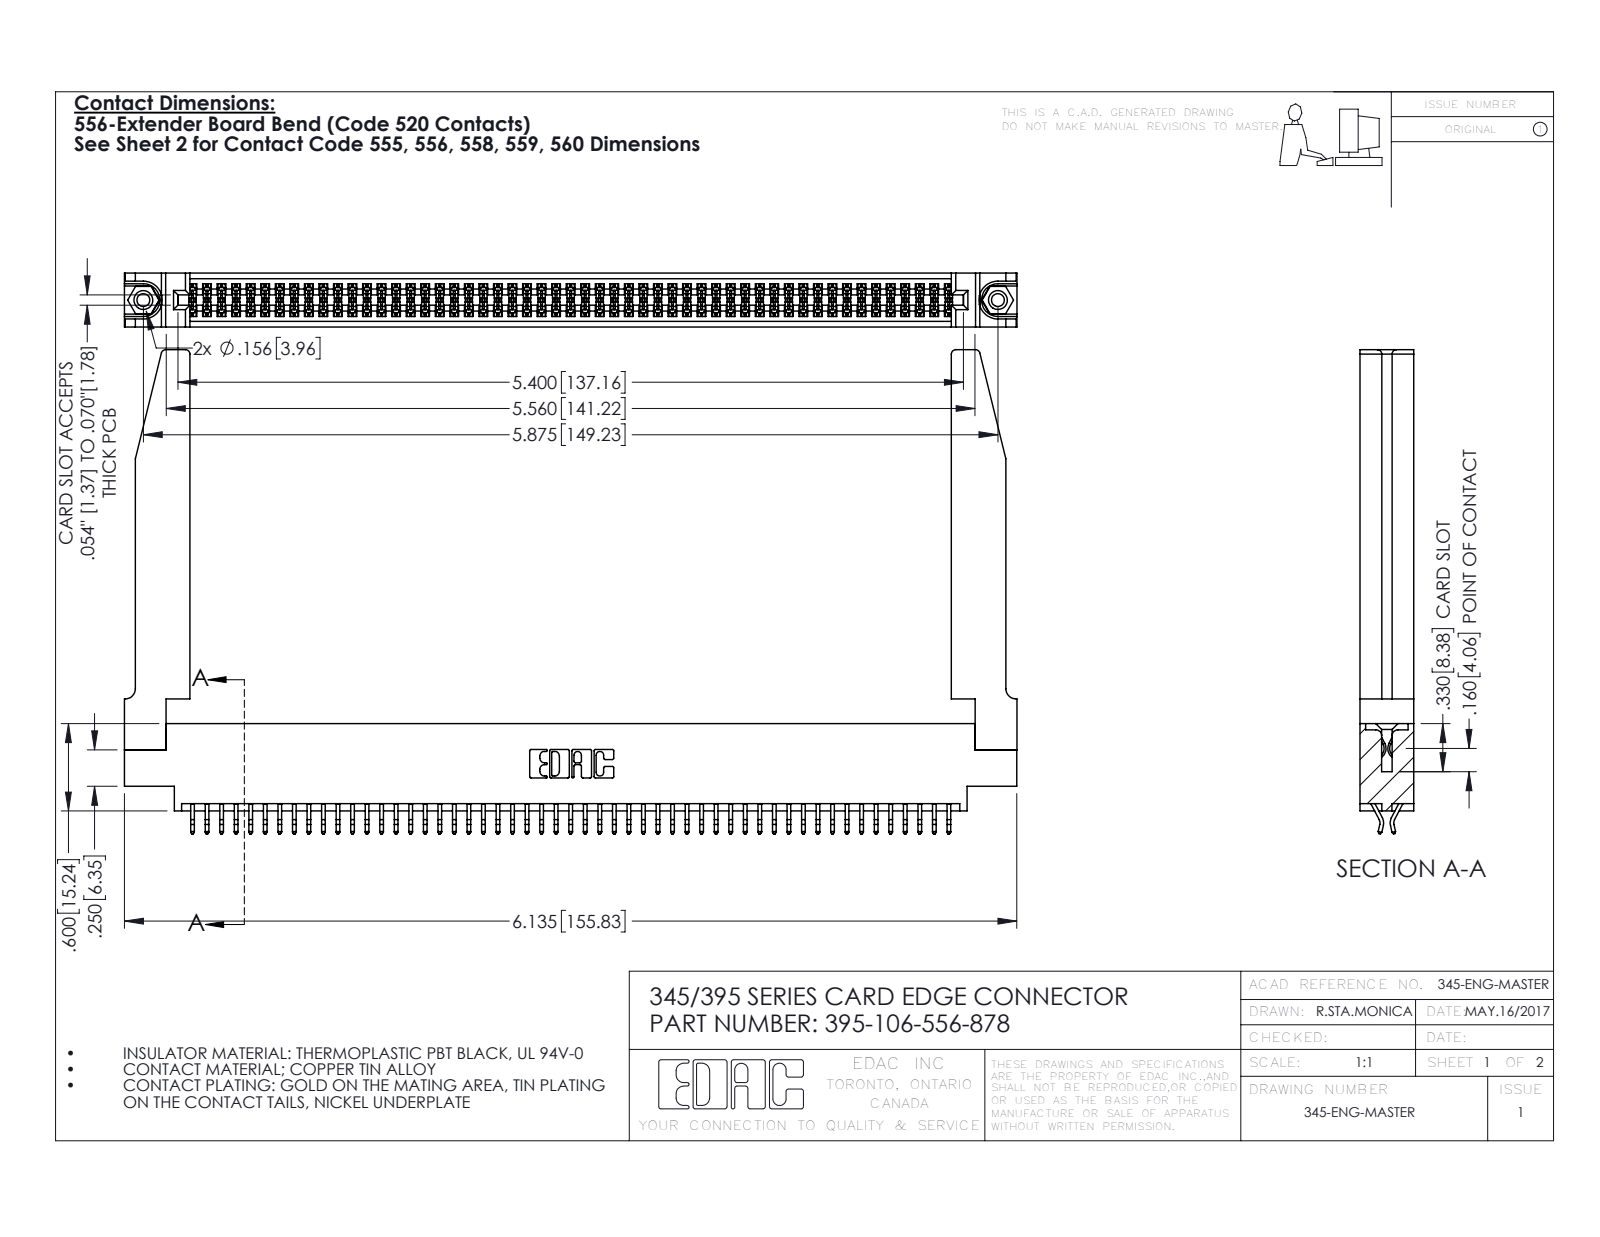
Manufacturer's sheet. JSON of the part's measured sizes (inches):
{"part_name": "345-292-001_556 Tail; 345-220-078_345-220-078; 345-250-001_345-250-001-102; 395-106-556-878 (+1 more)", "step_written_by": "SolidWorks 2016 (CONFIG_CONTROL_DESIGN)", "units": "inches", "bodies": {"solids": 111, "faces": 6300, "planar": 4148, "cylindrical": 2100, "other": 52}, "overall_size": [6.136, 3.327, 0.37], "volume_in3": 1.397, "surface_area_in2": 45.66, "round_holes": [[0.089, 2], [0.125, 2], [0.156, 2], [0.064, 1]], "round_bosses_or_shafts": [[0.155, 2]], "partial_cylinders_radius": [[0.006, 159], [0.01, 22], [0.03, 8], [0.007, 6], [0.031, 6], [0.026, 3], [0.01, 2], [0.014, 2]], "face_to_face_distances": [0.37, 0.072, 0.298, 0.025, 0.098, 0.272, 0.2, 0.225, 0.175, 0.148], "hole_center_spacings": [0.27, 5.639, 5.875]}
